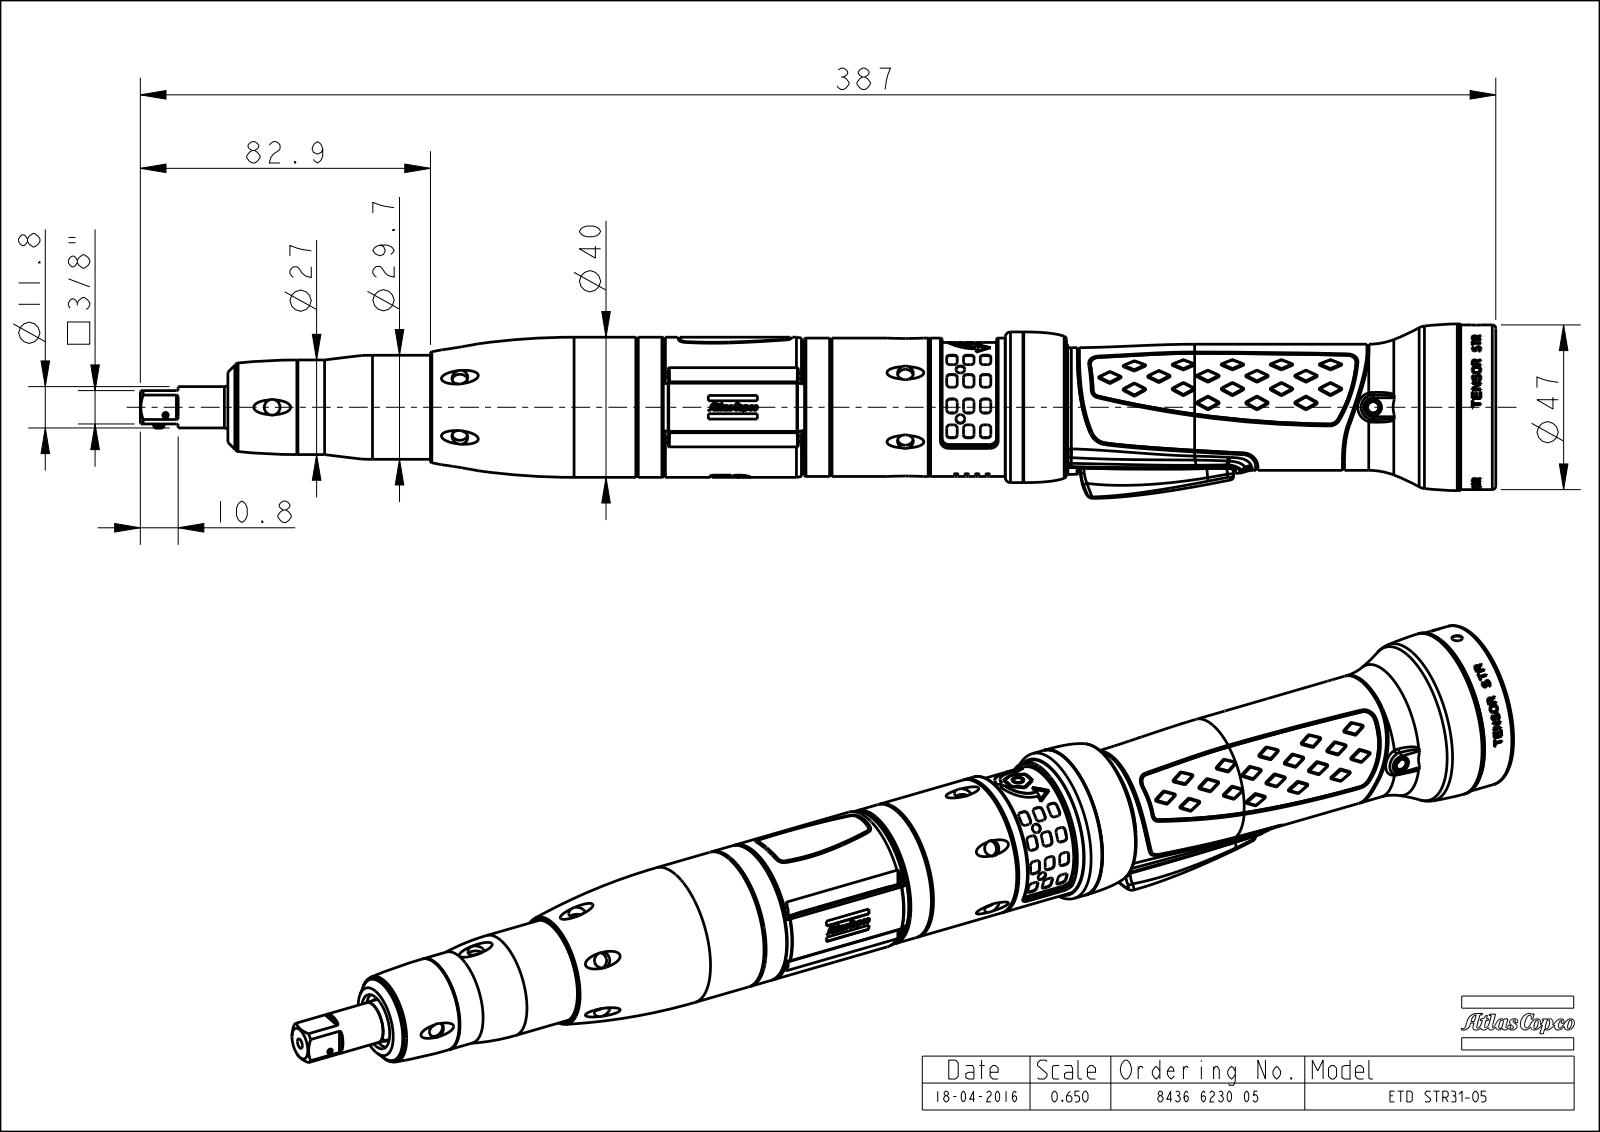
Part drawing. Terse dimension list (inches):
name: 4220502200; 4220518580-MONTERAD_ASM; 4220494580_ASM; 4220494780_ASM (+8 more)
written by: CREO PARAMETRIC BY PTC INC, 2014440 (CONFIG_CONTROL_DESIGN)
unit: in
bodies: 71 solids, 10046 faces (3914 planar, 1650 cylindrical, 4482 other)
size: 15.239 × 4.081 × 2.761
volume: 7.805 in³; area: 247.1 in²
holes: 33× ⌀0.02, 12× ⌀0.039, 12× ⌀0.105, 12× ⌀0.13, 10× ⌀0.142, 9× ⌀0.024, 8× ⌀0.177, 5× ⌀0.031, 5× ⌀0.067, 4× ⌀0.068, 4× ⌀0.102, 2× ⌀0.063
bosses: 9× ⌀0.12, 9× ⌀0.1, 9× ⌀0.096, 9× ⌀0.089, 9× ⌀0.061, 5× ⌀0.104, 5× ⌀0.063, 4× ⌀0.091
rounds: 157× R0.008, 65× R0.02, 62× R0.004, 51× R0.012, 18× R0.044, 18× R0.048, 16× R0.079, 12× R0.118
face distances: 0.034, 1.261, 0.035, 0.098, 0.906, 5.457, 1.295, 1.227, 0.059, 3.906
hole spacings: 0.189, 0.118, 0.378, 0.236, 0.176, 0.305, 0.591, 0.173
